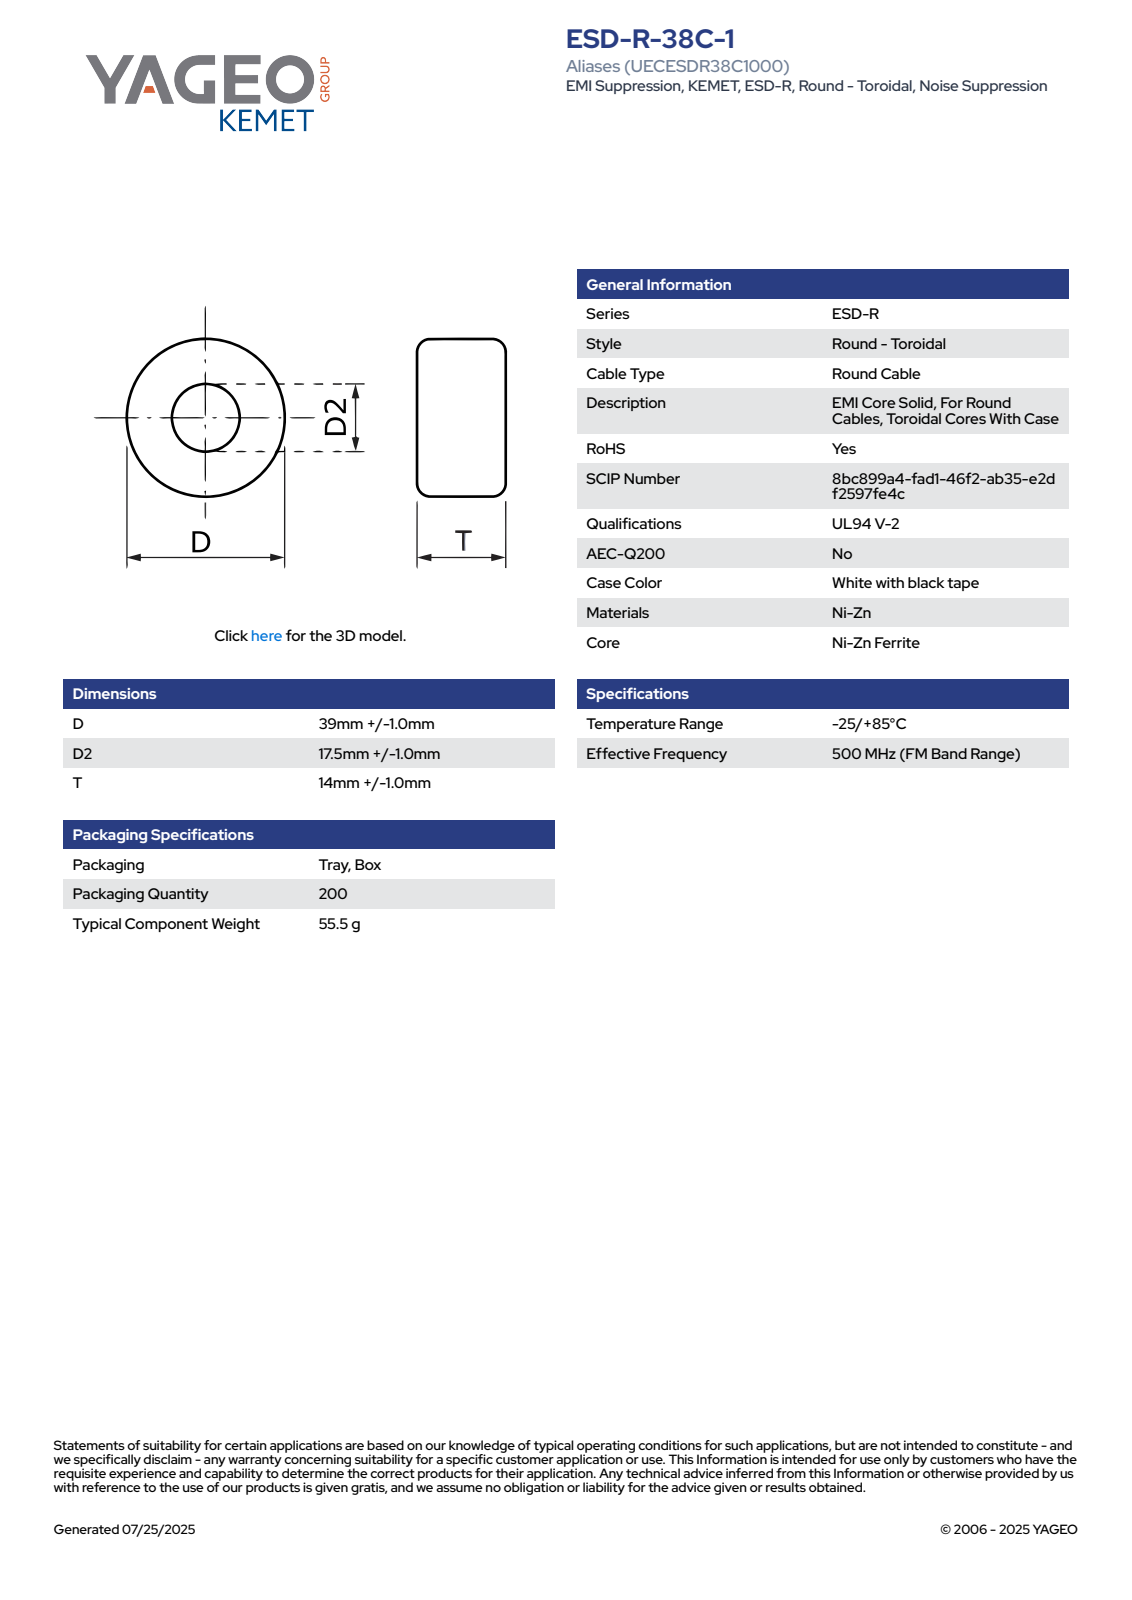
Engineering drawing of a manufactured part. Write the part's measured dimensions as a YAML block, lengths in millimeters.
part_name: "EC_KBC_D40D217.5T15"
step_written_by: "SolidWorks 2021 (AUTOMOTIVE_DESIGN)"
units: millimeters
bodies: {solids: 1, faces: 66, planar: 24, cylindrical: 7, other: 35}
overall_size: [40.01, 40, 15]
volume: 15158
surface_area: 4619
round_holes:
  - {diameter: 17.5, count: 1}
round_bosses_or_shafts:
  - {diameter: 40, count: 1}
partial_cylinders:
  - {radius: 20.01, count: 1}
face_to_face_distances: [15, 6.65, 8.35, 1.7, 0.32, 6.97, 8.03, 1.38, 1.06, 7.71]
